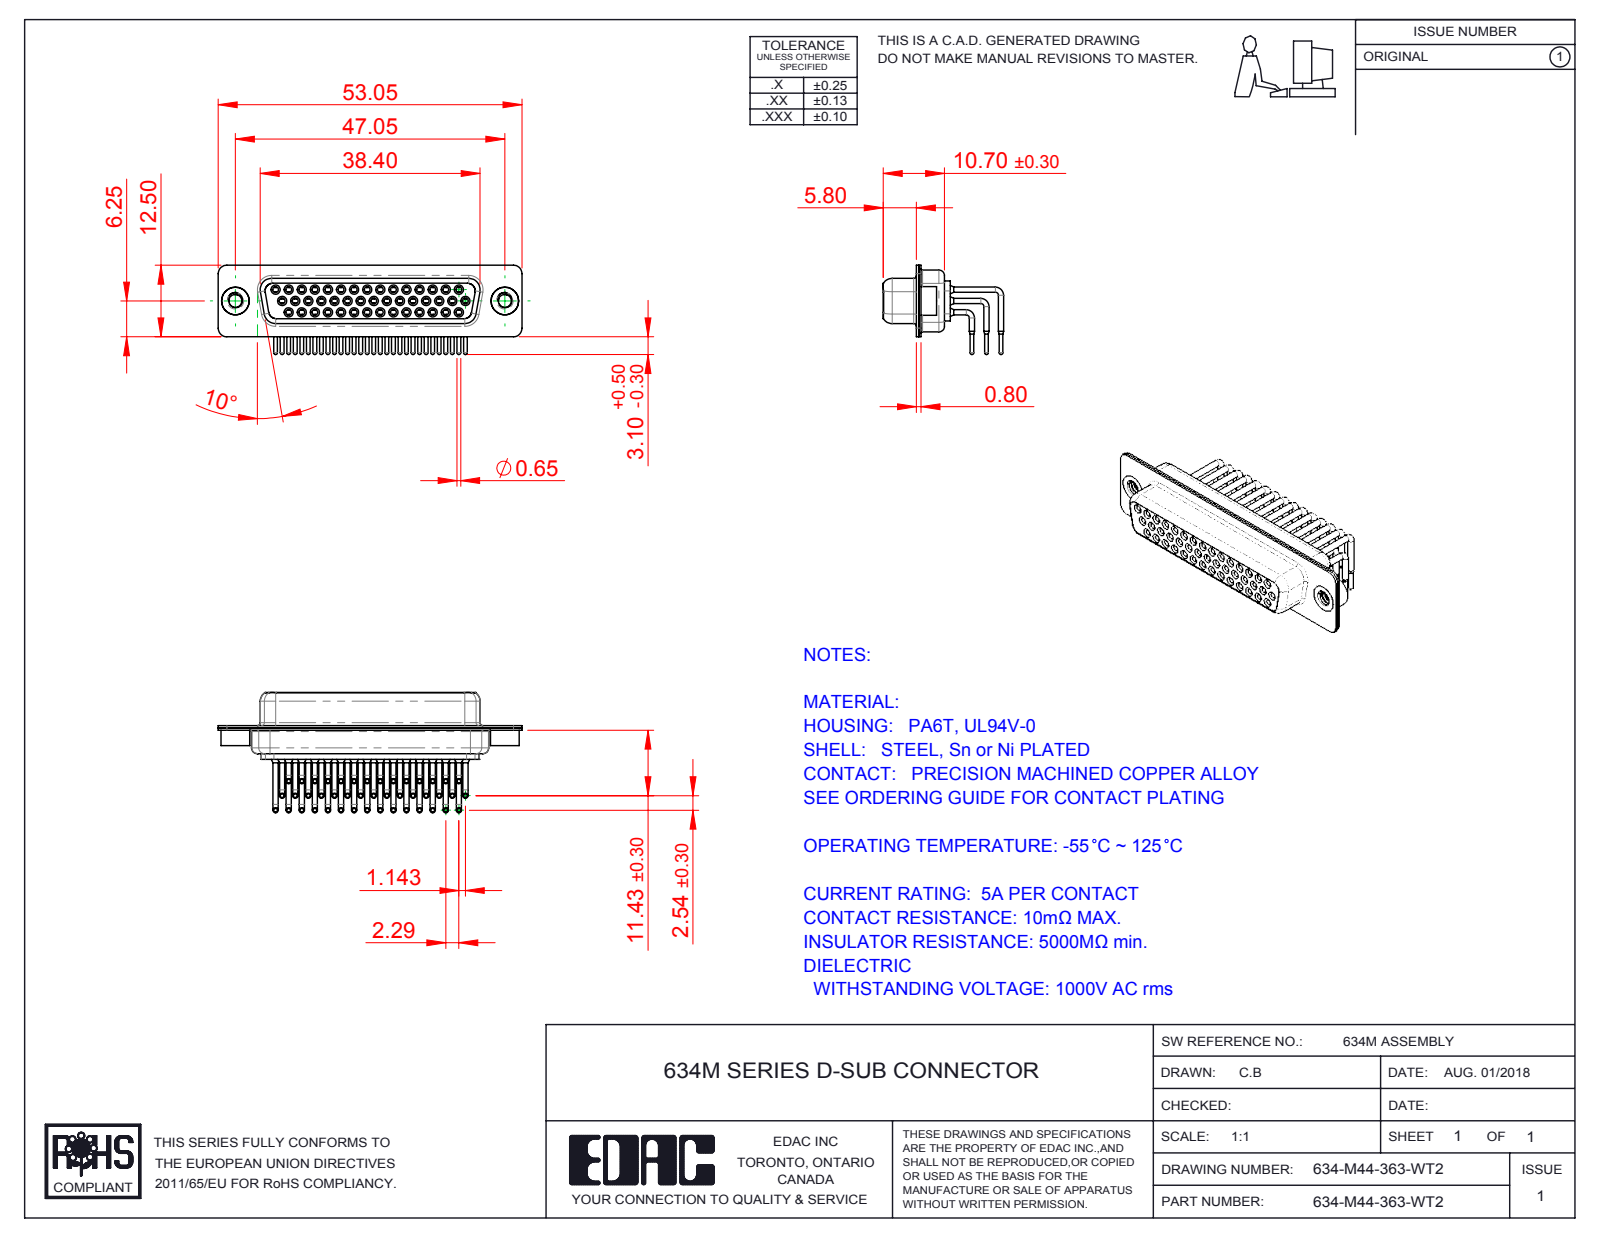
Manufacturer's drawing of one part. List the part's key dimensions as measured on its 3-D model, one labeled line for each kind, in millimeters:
Part name (STEP PRODUCT): 634M Contact Row 1; 634M Shell Rear_44 Contacts; 634-M44-363-WT2; 634M Contact Row 2 (+4 more)
STEP written by: SolidWorks 2016 (CONFIG_CONTROL_DESIGN)
Units: millimetres
Bodies: 49 solids, 2611 faces (727 planar, 1149 cylindrical, 735 other)
Overall size (bounding box): 53.05 × 21.02 × 15.6
Volume: 3 837 mm³ · Surface area: 13 038 mm²
Round holes (diameter × count): ⌀1 ×44, ⌀1.1 ×44, ⌀1.7 ×44, ⌀1.8 ×44, ⌀2 ×44, ⌀2.26 ×2, ⌀4 ×2, ⌀4.8 ×2
Round bosses / shafts (diameter × count): ⌀0.9 ×88, ⌀1.6 ×44, ⌀1.5 ×44, ⌀0.65 ×44, ⌀5 ×2, ⌀4.9 ×2
Partial cylindrical surfaces — rounded edges, fillets, slot ends (radius × count): R1.5 ×16, R2 ×12, R1.35 ×8, R1.6 ×8, R0.25 ×4, R0.5 ×4, R0.6 ×4, R0.65 ×4
Main face-to-face distances: 0.4, 1.45, 8.95, 2.3, 1.9, 8.5, 6.2, 7.05, 0.45, 0.85
Hole centre spacings: 2.28, 3.96, 2.29, 4.57, 8.24, 6.86, 11.43, 10.48
